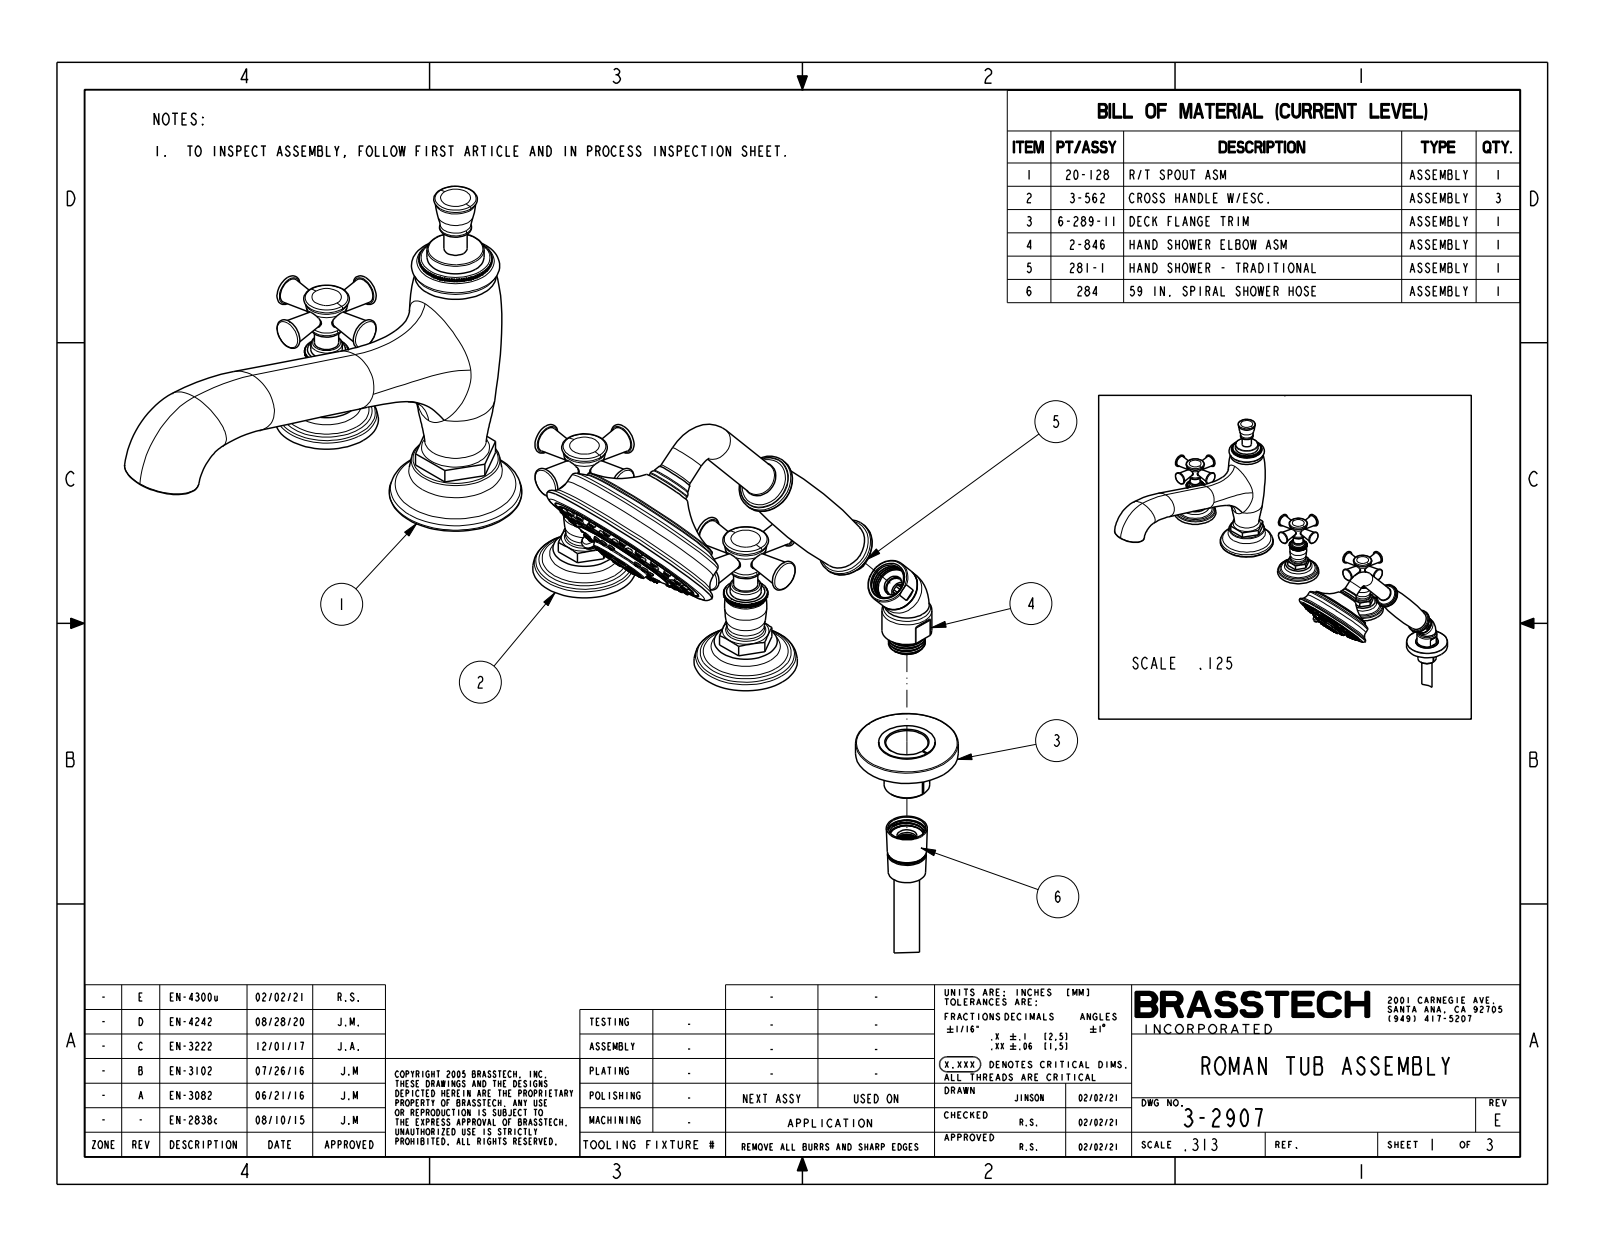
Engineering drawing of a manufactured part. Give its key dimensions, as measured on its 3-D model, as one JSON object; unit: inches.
{"part_name": "3-2907", "step_written_by": "CREO PARAMETRIC BY PTC INC, 2018400 (CONFIG_CONTROL_DESIGN)", "units": "inches", "bodies": {"solids": 5, "faces": 2702, "planar": 977, "cylindrical": 204, "other": 1521}, "overall_size": [21.375, 11.244, 7.987], "volume_in3": 69.02, "surface_area_in2": 259, "round_holes": [[0.059, 8]], "round_bosses_or_shafts": [[0.142, 39], [0.165, 23], [0.98, 4], [0.686, 3], [0.53, 3], [0.75, 2], [3.81, 1], [3.24, 1]], "partial_cylinders_radius": [[0.05, 6], [0.02, 4], [0.138, 1], [0.472, 1], [0.512, 1], [1.862, 1]], "face_to_face_distances": [0.3, 0.534, 0.234, 6.583, 6.283, 6.05, 1.025, 1.575, 0.394, 2.164], "hole_center_spacings": [0.443, 0.819, 1.069, 1.157, 0.818, 1.07, 0.443, 0.443]}
